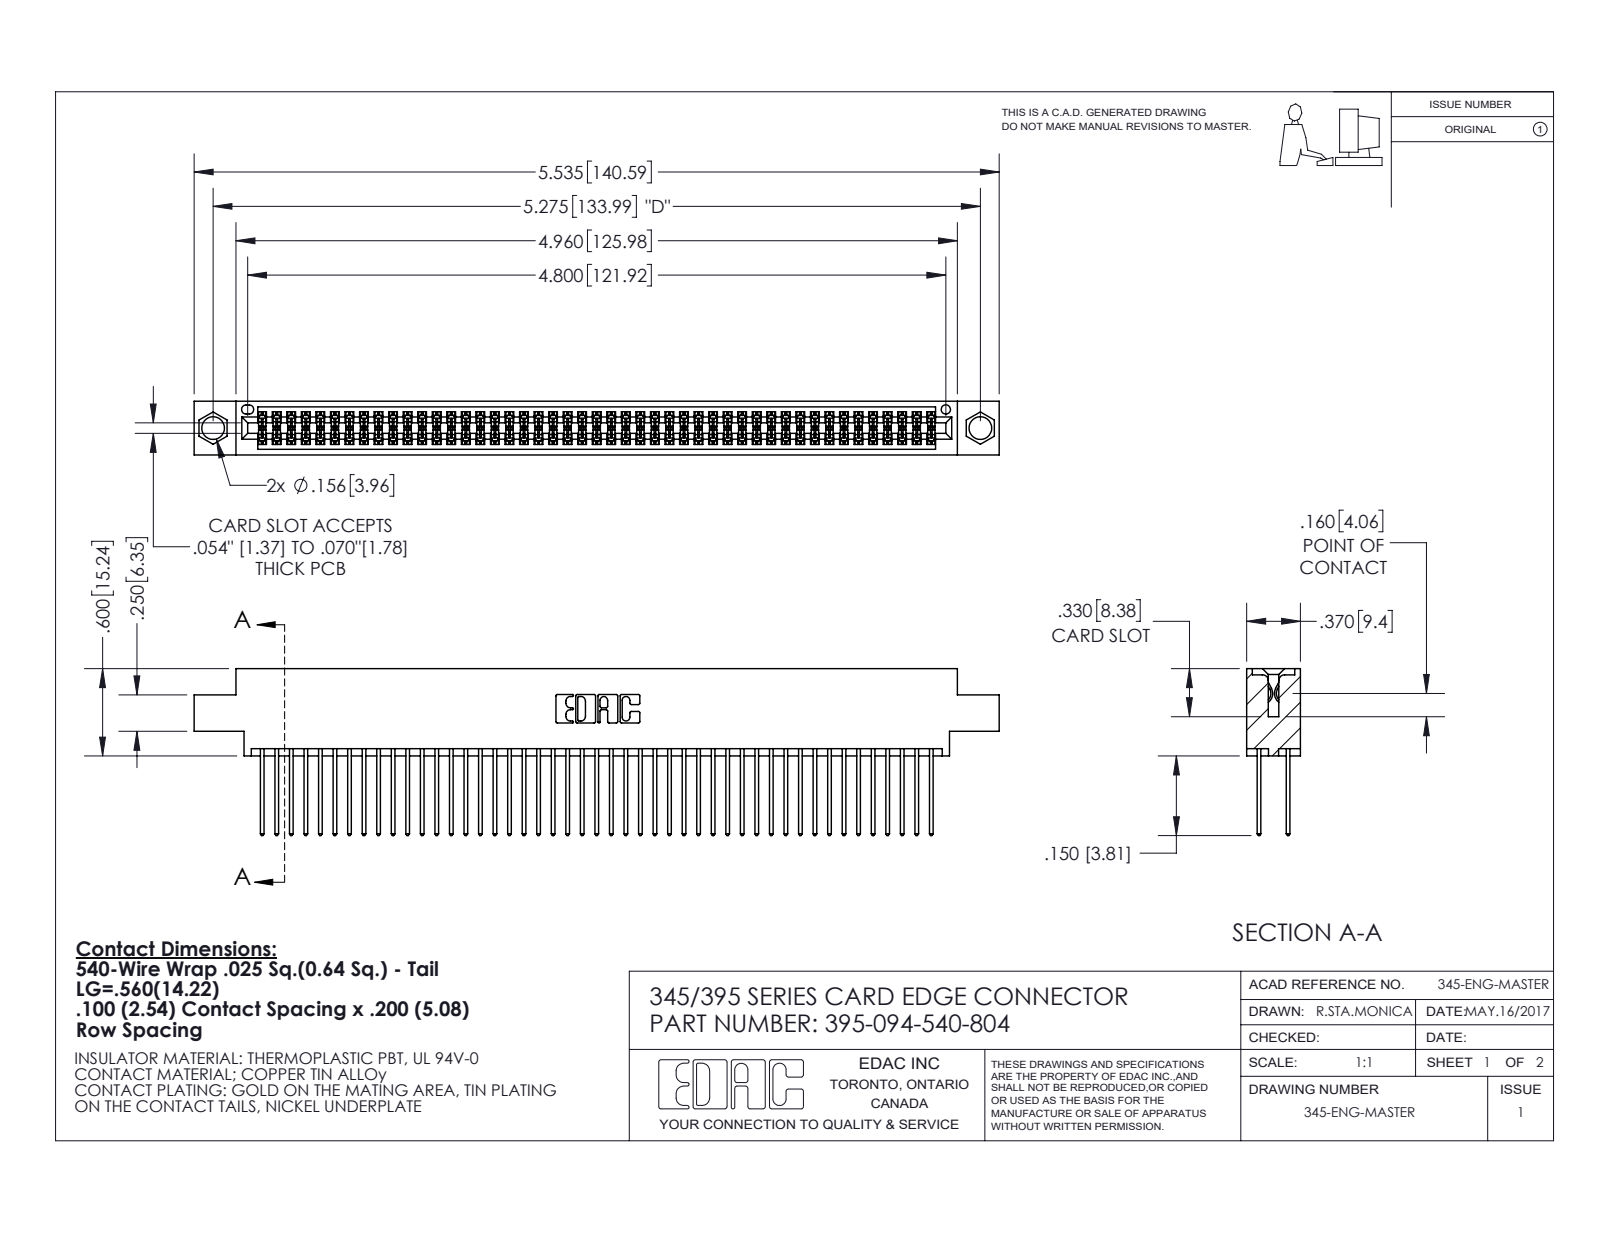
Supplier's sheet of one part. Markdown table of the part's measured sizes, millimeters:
| quantity | value |
| --- | --- |
| part name | 345-292-001_345-293-140; 395-094-540-804; 345 Part_0.170 Offset - 0.156 Dia-TI |
| STEP written by | SolidWorks 2020 (CONFIG_CONTROL_DESIGN) |
| units | millimeters |
| bodies | 95 solids, 4844 faces (3200 planar, 1644 cylindrical, 0 other) |
| overall size | 140.6 × 29.1 × 9.4 |
| volume | 13 800 mm³ |
| surface area | 22 210 mm² |
| round holes (diameter × count) | 4 × 2, 1.6 × 1 |
| partial cylindrical surfaces (radius × count) | 0.2 × 188, 0.3 × 94, 0.3 × 22, 0.2 × 6, 0.8 × 6, 0.7 × 3, 0.4 × 2, 0.5 × 2 |
| main face-to-face distances | 1.8, 7.6, 5.1, 2.5, 6.9, 0.6, 9.4, 5.7, 4.4, 3.8 |
| hole center spacings | 6.9, 128, 134 |
